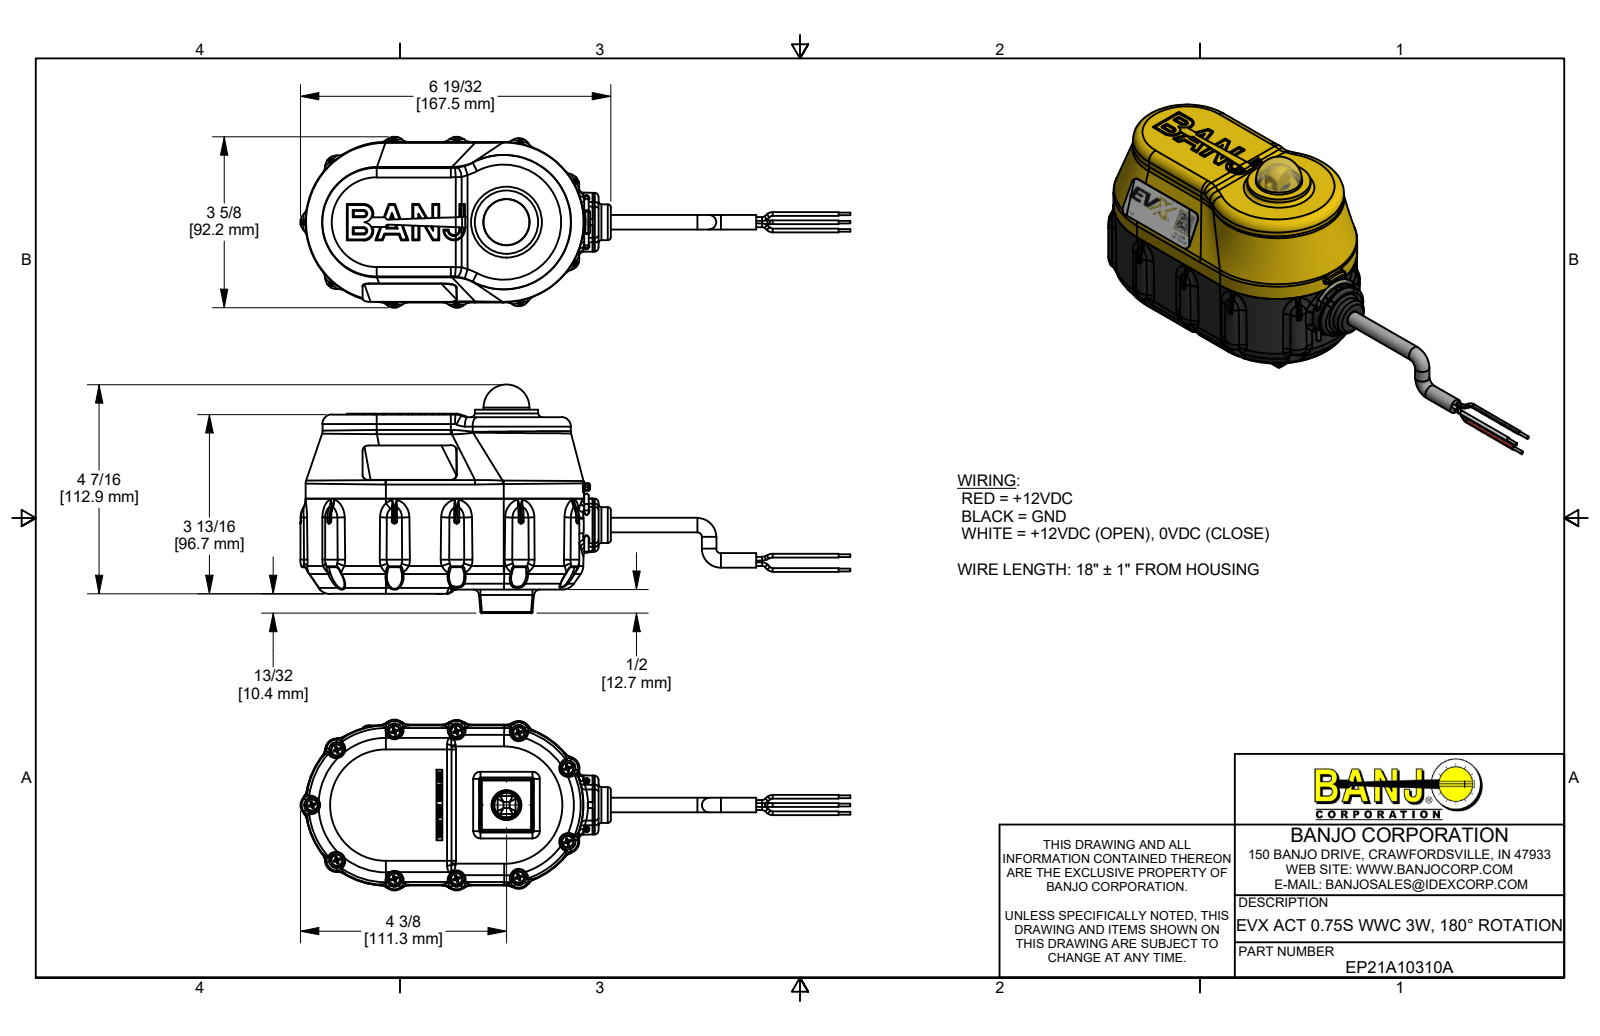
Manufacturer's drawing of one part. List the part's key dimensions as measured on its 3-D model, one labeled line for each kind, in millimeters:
Part name (STEP PRODUCT): EP21A10310A; B61905PPHS; B632038PM; EP10310A (+8 more)
STEP written by: Autodesk Inventor 2019 (AUTOMOTIVE_DESIGN)
Units: millimetres
Bodies: 73 solids, 10058 faces (2588 planar, 2949 cylindrical, 4521 other)
Overall size (bounding box): 296.8 × 123.3 × 92.2
Volume: 511 100 mm³ · Surface area: 261 500 mm²
Round holes (diameter × count): ⌀2.4 ×11, ⌀3.8 ×11, ⌀2 ×7, ⌀2.7 ×4, ⌀3.2 ×4, ⌀3.5 ×4, ⌀3.8 ×4, ⌀3.8 ×4, ⌀4.3 ×4, ⌀2.7 ×2, ⌀3 ×2, ⌀3.1 ×2
Round bosses / shafts (diameter × count): ⌀6.4 ×17, ⌀2 ×15, ⌀3.6 ×11, ⌀2.7 ×11, ⌀2.2 ×11, ⌀1.5 ×6, ⌀6.9 ×4, ⌀5.6 ×4
Partial cylindrical surfaces — rounded edges, fillets, slot ends (radius × count): R0.3 ×180, R1 ×145, R0.3 ×80, R0.5 ×71, R0.1 ×50, R0.8 ×37, R0.4 ×28, R2 ×28
Main face-to-face distances: 2.5, 65.2, 5.4, 1.5, 3.8, 42.8, 46.6, 48.2, 62.6, 19.8
Hole centre spacings: 32.6, 38.4, 68.3, 72.4, 96.2, 12.4, 17, 31.1
